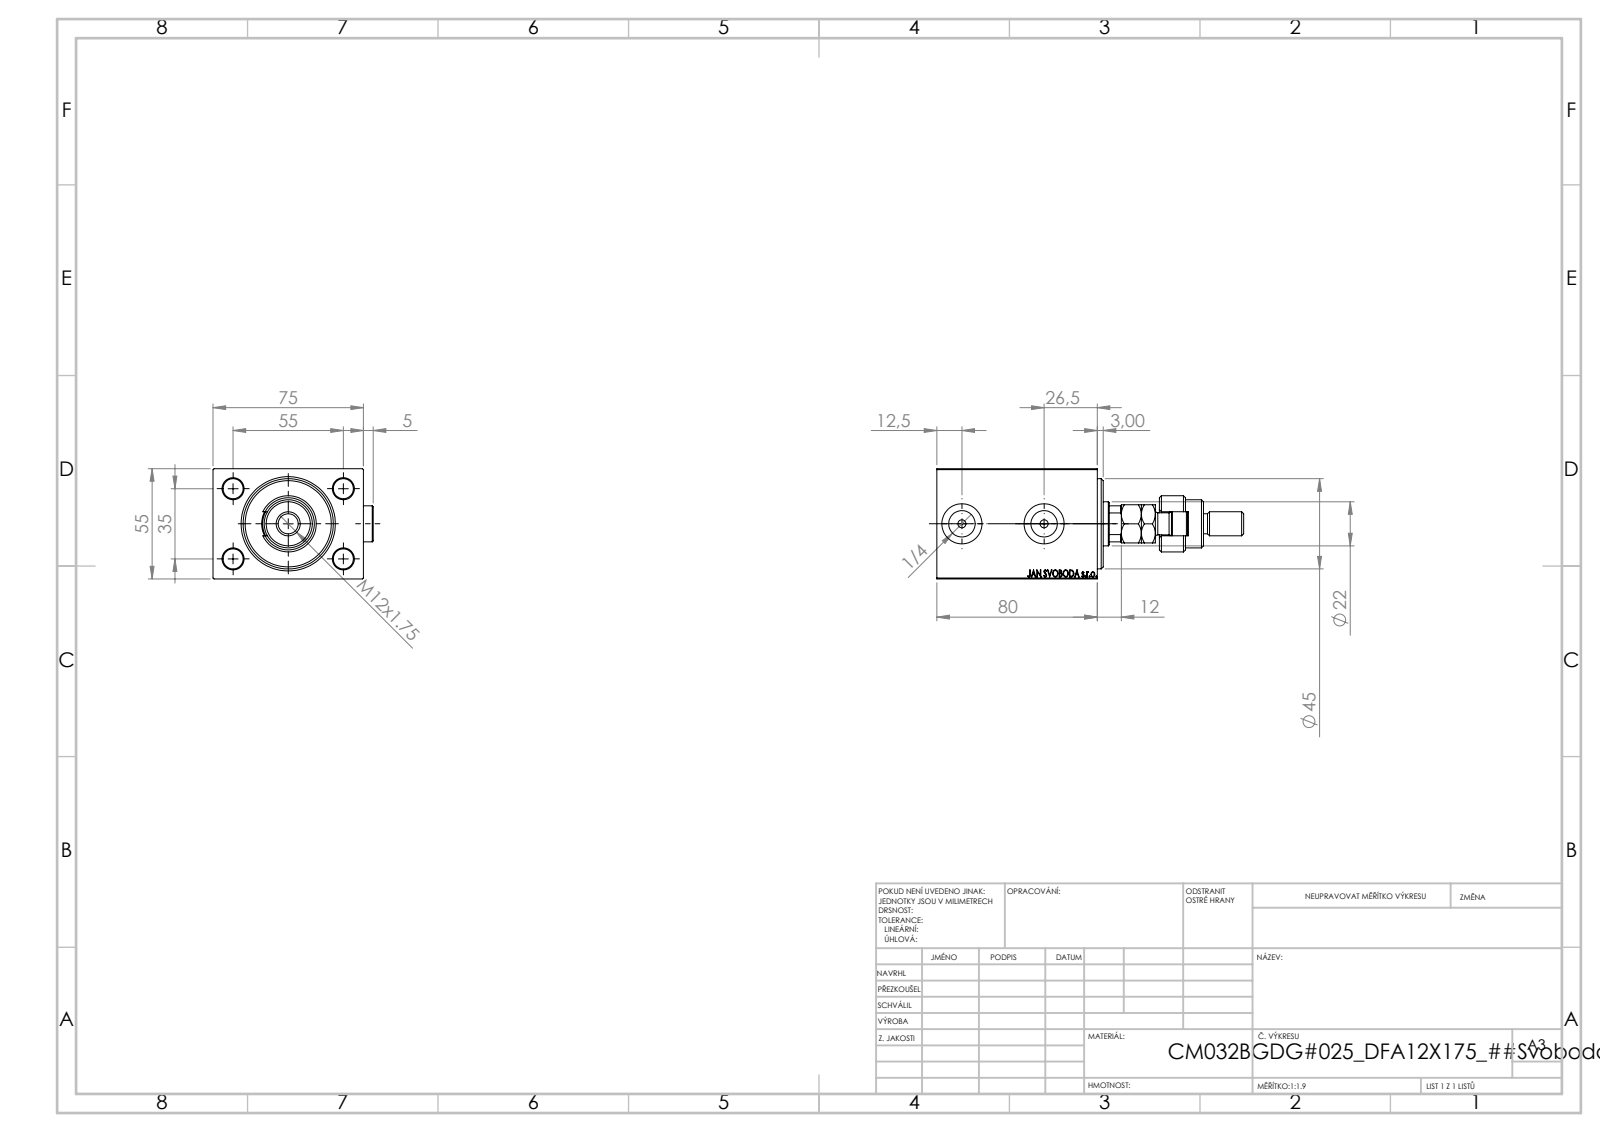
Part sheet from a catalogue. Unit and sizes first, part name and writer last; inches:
Units: inches
Overall size (bounding box): 6.024 × 3.146 × 2.165
Round holes (diameter × count): ⌀0.394 ×4, ⌀0.157 ×2, ⌀0.518 ×2, ⌀0.787 ×2, ⌀0.413 ×1, ⌀0.866 ×1, ⌀1.004 ×1, ⌀1.043 ×1, ⌀1.26 ×1, ⌀1.339 ×1, ⌀1.772 ×1
Round bosses / shafts (diameter × count): ⌀0.709 ×3, ⌀1.102 ×1, ⌀0.945 ×1, ⌀0.472 ×1, ⌀0.433 ×1, ⌀0.394 ×1
Partial cylindrical surfaces — rounded edges, fillets, slot ends (radius × count): R0.384 ×1, R0.413 ×1
Main face-to-face distances: 2.165, 2.953, 3.15, 0.197, 2.756, 2.559, 0.394, 0.315, 2.949, 0.472
Hole centre spacings: 1.283, 1.378, 2.165, 2.567, 1.614
Volume: 19.8 in³ · Surface area: 103.5 in²
Bodies: 7 solids, 1020 faces (463 planar, 83 cylindrical, 474 other)
Part name (STEP PRODUCT): V450CM_VC_B; V450CM_B_Body; V450CM_B_VCP; MFA (+2 more)
STEP written by: SolidWorks 2019 (CONFIG_CONTROL_DESIGN)
